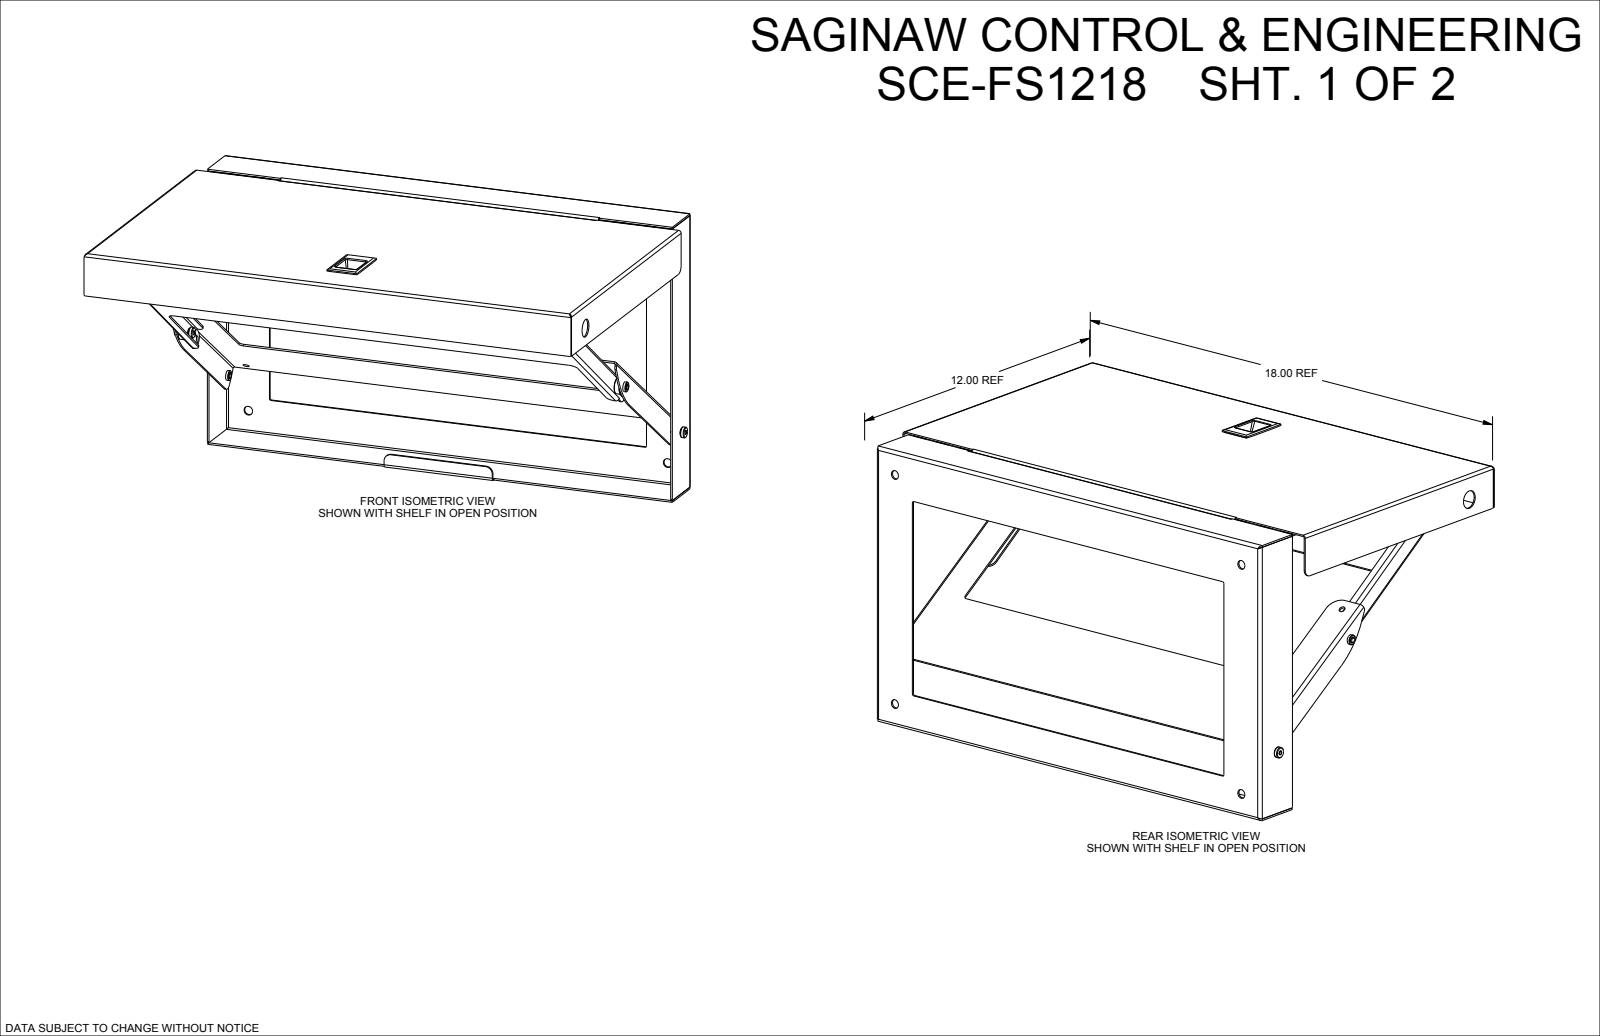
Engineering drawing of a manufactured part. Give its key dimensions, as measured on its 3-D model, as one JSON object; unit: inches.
{"part_name": "SCE-FS1218", "step_written_by": "SolidWorks 2019 (CONFIG_CONTROL_DESIGN)", "units": "inches", "bodies": {"solids": 55, "faces": 1801, "planar": 1120, "cylindrical": 312, "other": 369}, "overall_size": [18, 12, 9.99], "volume_in3": 31.28, "surface_area_in2": 1151, "round_holes": [[0.19, 15], [0.193, 12], [0.203, 8], [0.218, 6], [0.22, 4], [0.313, 4], [0.25, 3], [0.265, 3], [0.187, 2], [0.257, 2], [0.265, 2], [0.125, 1]], "round_bosses_or_shafts": [[0.188, 15], [0.256, 12], [0.55, 3], [0.371, 3], [0.34, 3], [0.249, 3], [0.246, 3], [0.245, 1]], "partial_cylinders_radius": [[0.25, 20], [0.014, 16], [0.125, 13], [0.052, 12], [0.112, 12], [0.031, 7], [0.04, 7], [0.03, 6]], "face_to_face_distances": [0.048, 0.06, 0.06, 0.048, 9.846, 17.128, 0.012, 9.787, 9.834, 9.894], "hole_center_spacings": [0.874, 1.5, 1.736, 14.438, 14.464, 0.875, 2.244, 5.981]}
